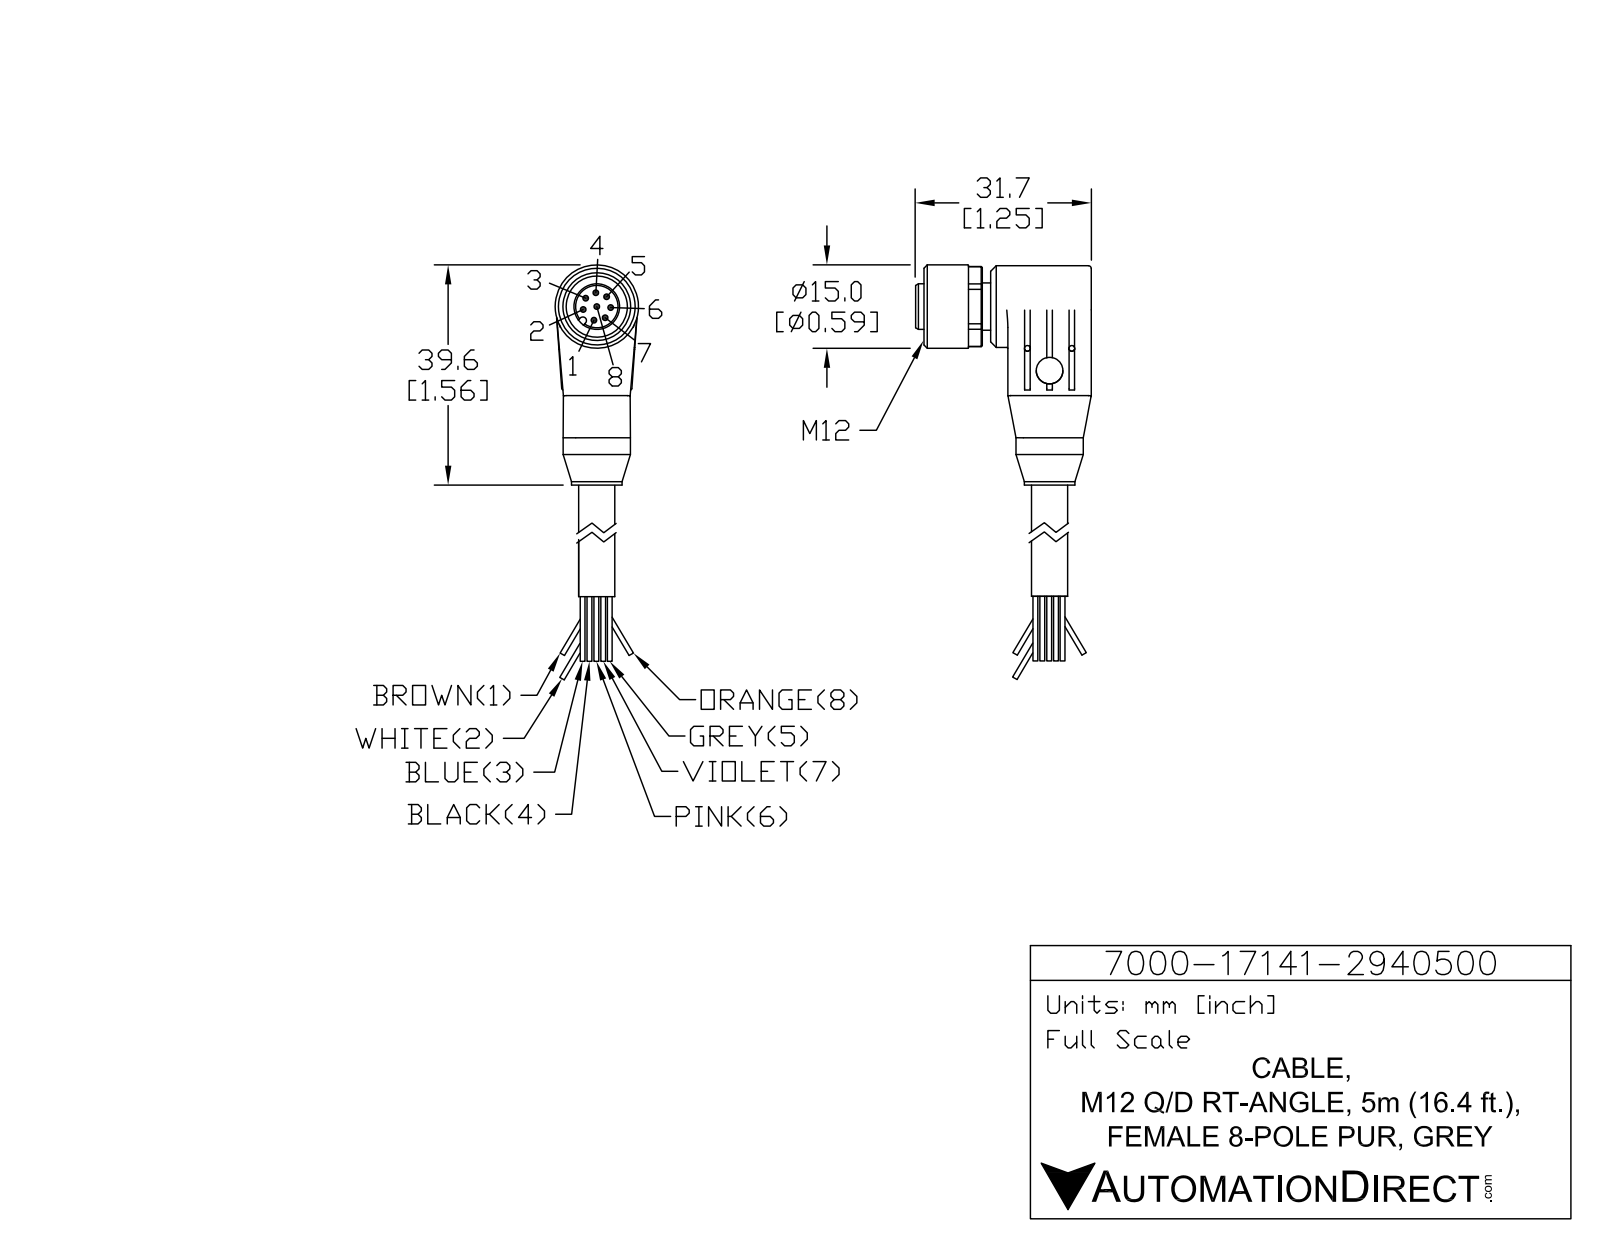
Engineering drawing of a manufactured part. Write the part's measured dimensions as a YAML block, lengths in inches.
part_name: "7000-17141-2940500"
step_written_by: "SolidWorks 2015 (AUTOMOTIVE_DESIGN)"
units: inches
bodies: {solids: 1, faces: 174, planar: 73, cylindrical: 67, other: 34}
overall_size: [2.346, 1.248, 0.591]
volume: 0.555
surface_area: 6.33
round_holes:
  - {diameter: 0.039, count: 8}
  - {diameter: 0.041, count: 4}
  - {diameter: 0.189, count: 1}
  - {diameter: 0.433, count: 1}
round_bosses_or_shafts:
  - {diameter: 0.591, count: 1}
  - {diameter: 0.579, count: 1}
  - {diameter: 0.476, count: 1}
  - {diameter: 0.358, count: 1}
  - {diameter: 0.335, count: 1}
  - {diameter: 0.323, count: 1}
  - {diameter: 0.256, count: 1}
partial_cylinders:
  - {radius: 0.02, count: 4}
  - {radius: 0.012, count: 2}
  - {radius: 0.026, count: 1}
  - {radius: 0.283, count: 1}
face_to_face_distances: [0.098, 0.591, 0.185, 0.689, 0.776, 0.087, 0.118, 0.303, 0.472, 0.657]
hole_center_spacings: [0.098, 0.081, 0.149, 0.195, 0.082, 0.166, 0.189, 0.189]
